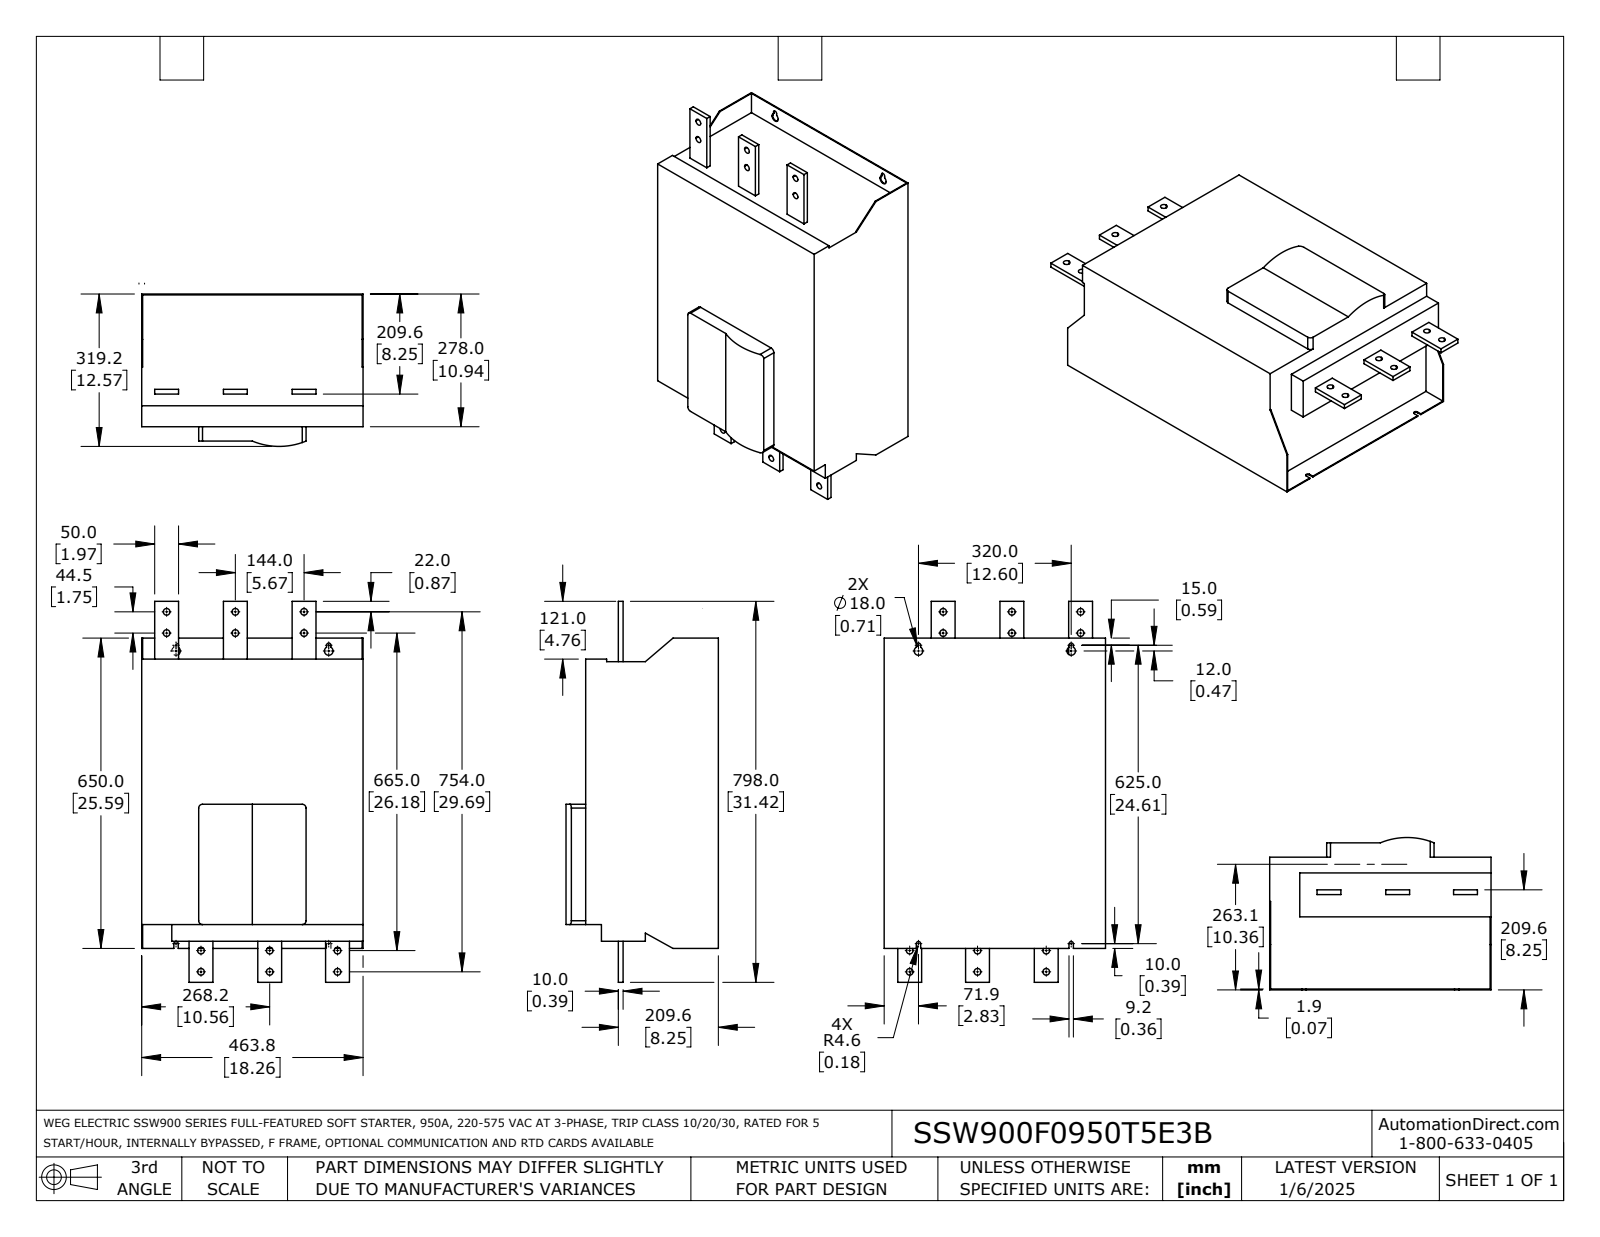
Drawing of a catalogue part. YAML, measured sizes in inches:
part_name: "SSW900F0950T5E3B"
step_written_by: "SolidWorks 2021 (AUTOMOTIVE_DESIGN)"
units: inches
bodies: {solids: 1, faces: 107, planar: 68, cylindrical: 39, other: 0}
overall_size: [31.417, 18.26, 12.568]
volume: 4561
surface_area: 2117
round_holes:
  - {diameter: 0.551, count: 12}
  - {diameter: 0.709, count: 2}
partial_cylinders:
  - {radius: 0.181, count: 4}
  - {radius: 0.315, count: 4}
  - {radius: 5.788, count: 1}
face_to_face_distances: [10.945, 18.26, 21.676, 0.075, 10.87, 1.378, 23.054, 7.858, 8.252, 7.783]
hole_center_spacings: [28.076, 1.752, 5.669, 5.934, 26.334, 29.199, 29.82, 5.594]
